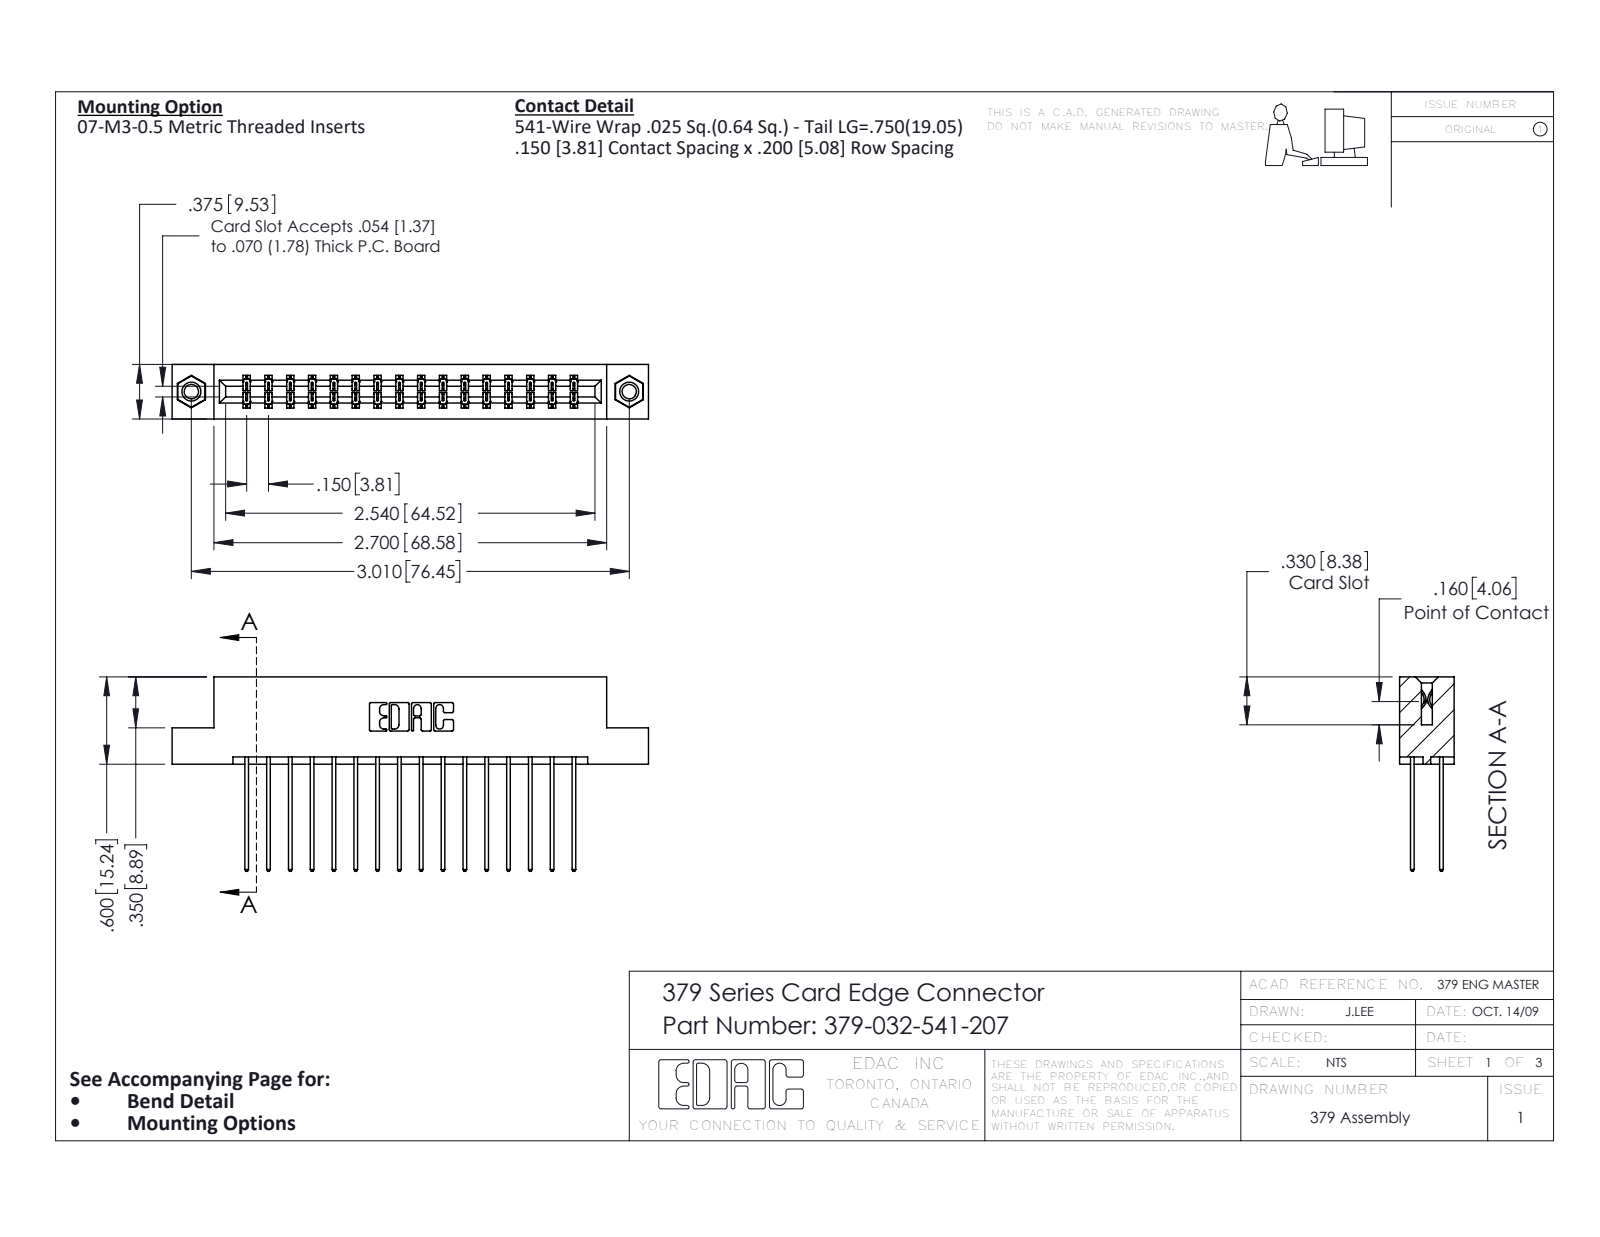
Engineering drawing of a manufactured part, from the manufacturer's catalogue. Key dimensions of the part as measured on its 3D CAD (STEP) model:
Part name (STEP PRODUCT): 379-032-541-207; 379 Part_Flush - .156 Dia - TI; 345-292-001_345-293-141; 345-250-001_345-250-005-103
STEP written by: SolidWorks 2020 (CONFIG_CONTROL_DESIGN)
Units: inches
Bodies: 35 solids, 1838 faces (1254 planar, 568 cylindrical, 16 other)
Overall size (bounding box): 3.275 × 1.337 × 0.375
Volume: 0.531 in³ · Surface area: 16.27 in²
Round holes (diameter × count): ⌀0.098 ×2, ⌀0.125 ×2, ⌀0.156 ×2
Round bosses / shafts (diameter × count): ⌀0.155 ×2
Partial cylindrical surfaces — rounded edges, fillets, slot ends (radius × count): R0.006 ×63, R0.01 ×32, R0.01 ×22, R0.007 ×6, R0.031 ×6, R0.026 ×3, R0.014 ×2, R0.022 ×2
Main face-to-face distances: 0.3, 0.075, 0.375, 0.6, 0.2, 0.275, 0.1, 0.15, 0.025, 0.076
Hole centre spacings: 3.01
